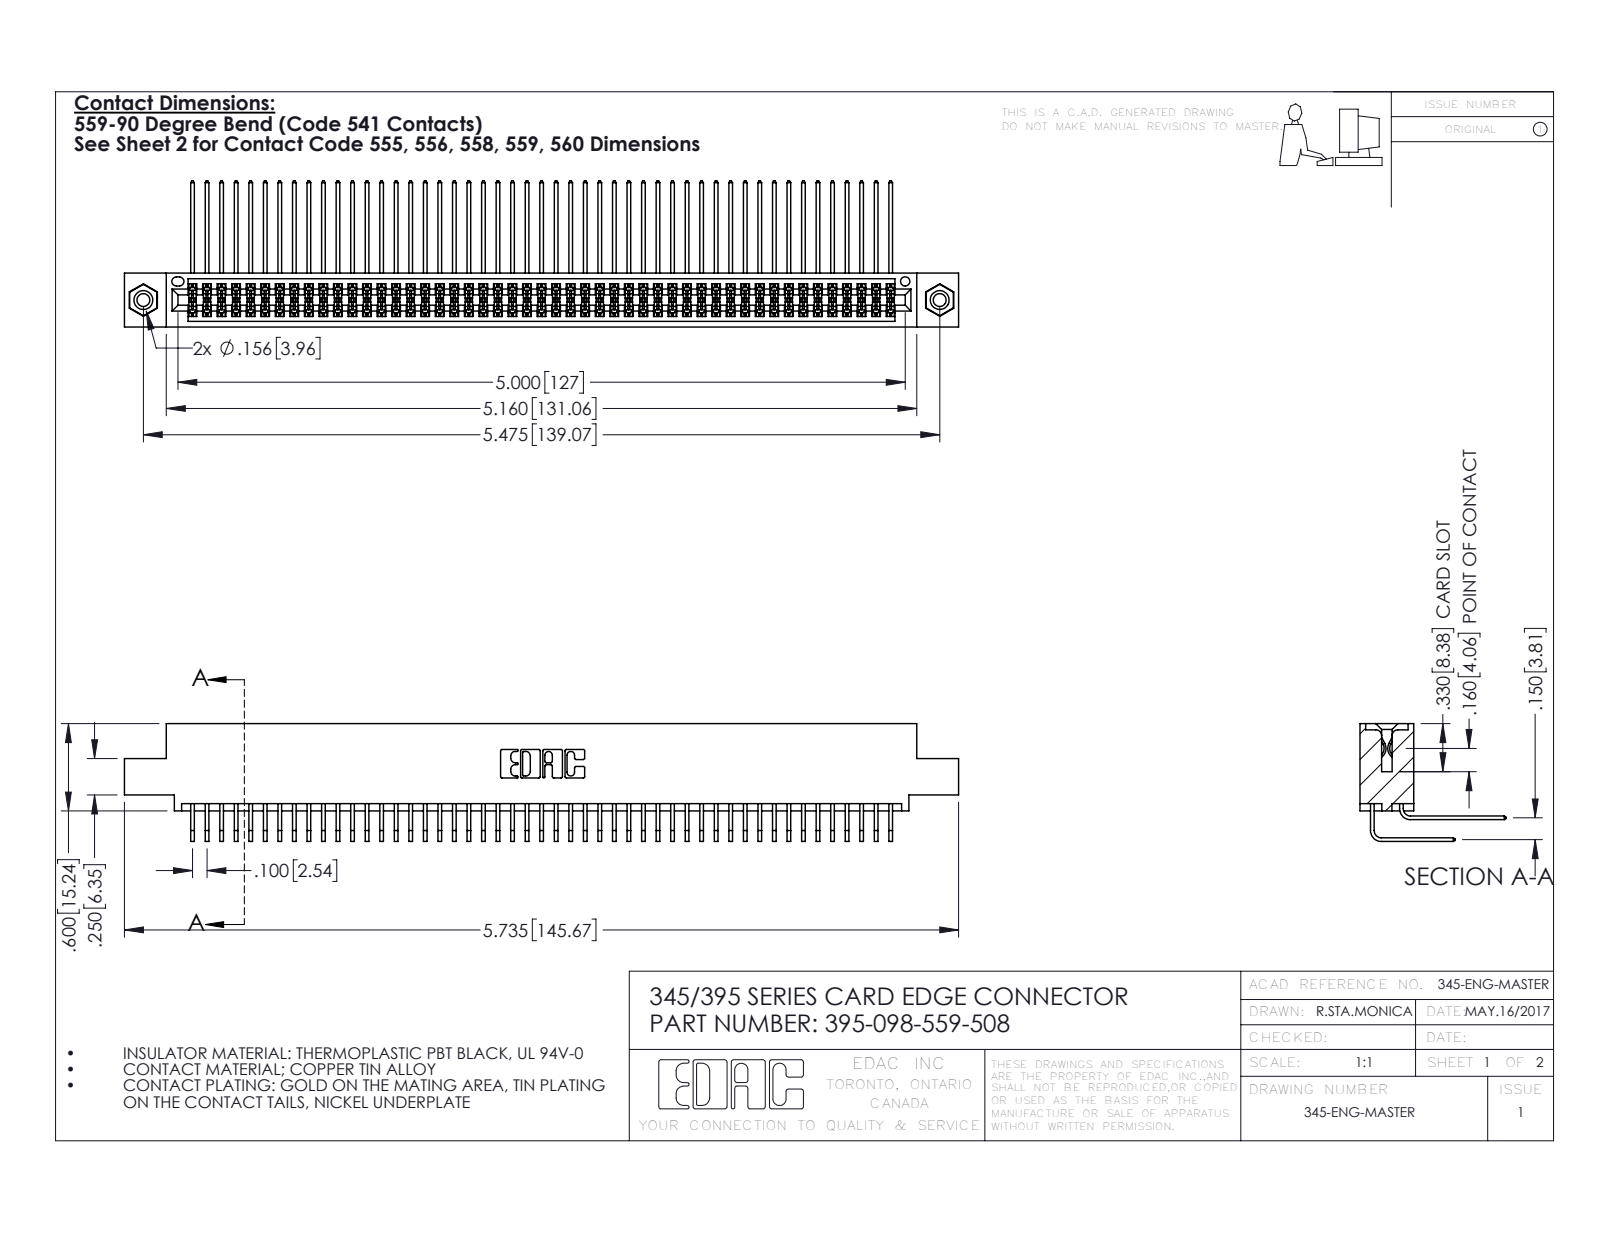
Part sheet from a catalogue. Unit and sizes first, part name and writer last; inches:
Units: inches
Overall size (bounding box): 5.735 × 1.005 × 0.809
Round holes (diameter × count): ⌀0.089 ×2, ⌀0.125 ×2, ⌀0.156 ×2, ⌀0.064 ×1
Round bosses / shafts (diameter × count): ⌀0.155 ×2
Partial cylindrical surfaces — rounded edges, fillets, slot ends (radius × count): R0.006 ×147, R0.01 ×22, R0.007 ×6, R0.031 ×6, R0.026 ×3, R0.014 ×2, R0.019 ×2, R0.022 ×2
Main face-to-face distances: 0.072, 0.298, 0.2, 0.37, 0.098, 0.272, 0.025, 0.225, 0.175, 0.15
Hole centre spacings: 0.27, 5.239, 5.475
Volume: 0.897 in³ · Surface area: 38.18 in²
Bodies: 101 solids, 5286 faces (3546 planar, 1724 cylindrical, 16 other)
Part name (STEP PRODUCT): 345-292-001_559 Tail - 2; 395-098-559-508; 345 Part_0.110 Offset - 0.156 Dia-TI; 345-292-001_558 559 Tail - 1 (+1 more)
STEP written by: SolidWorks 2016 (CONFIG_CONTROL_DESIGN)
